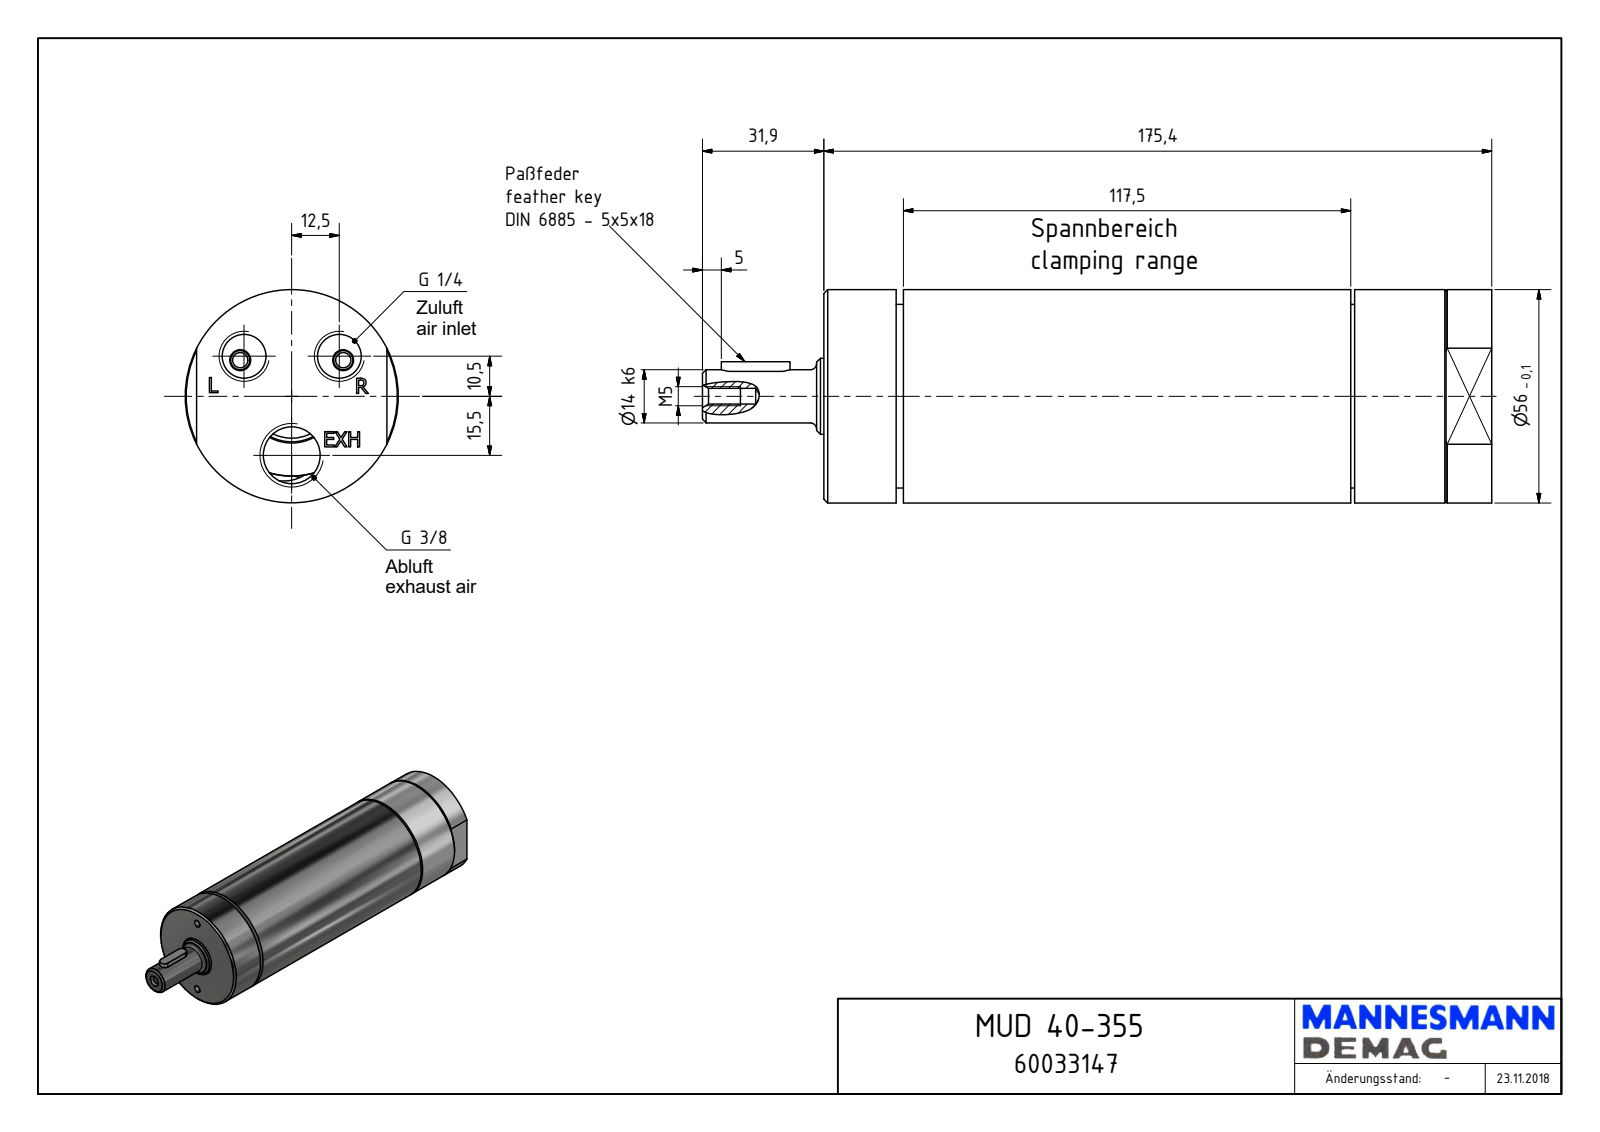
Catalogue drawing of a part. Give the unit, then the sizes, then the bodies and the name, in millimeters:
Units: millimetres
Overall size (bounding box): 207.3 × 56 × 56
Round holes (diameter × count): ⌀4 ×2, ⌀11.45 ×2, ⌀4.13 ×1, ⌀14.95 ×1, ⌀21 ×1, ⌀21.25 ×1, ⌀23.54 ×1, ⌀26 ×1, ⌀48.38 ×1
Round bosses / shafts (diameter × count): ⌀56 ×1, ⌀48.18 ×1, ⌀19.95 ×1, ⌀14 ×1
Partial cylindrical surfaces — rounded edges, fillets, slot ends (radius × count): R2.5 ×2, R6 ×2, R19.87 ×1, R23 ×1
Main face-to-face distances: 175.4, 20.9, 154.5, 138.4, 117.5, 37, 1.9, 139.4, 19, 119.4
Hole centre spacings: 16.32, 21, 28.85, 33.89, 5.5, 15.5, 25, 36.5
Volume: 429 188 mm³ · Surface area: 44 659 mm²
Bodies: 1 solid, 171 faces (92 planar, 32 cylindrical, 47 other)
Part name (STEP PRODUCT): MUD 40-355_60033147
STEP written by: Autodesk Inventor 2018 (AUTOMOTIVE_DESIGN)
